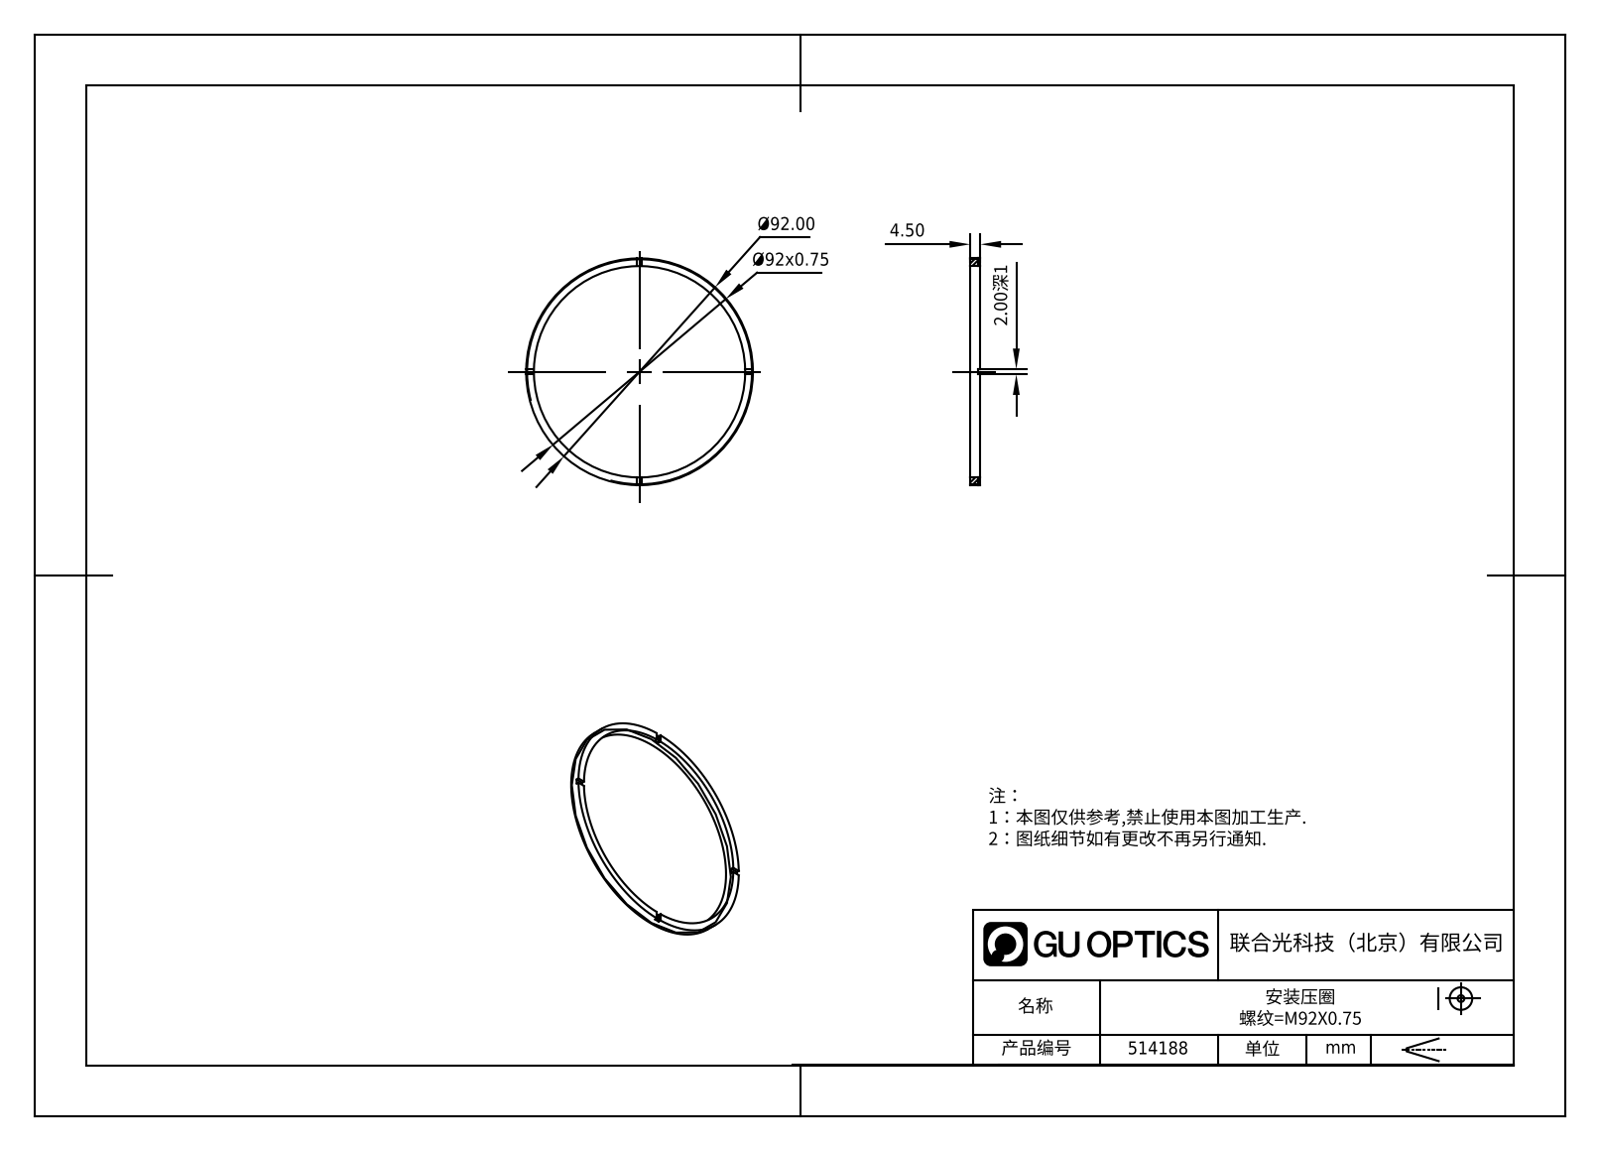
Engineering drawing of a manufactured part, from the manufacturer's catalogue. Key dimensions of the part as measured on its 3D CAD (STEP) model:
Part name (STEP PRODUCT): 514188
STEP written by: SolidWorks 2020 (CONFIG_CONTROL_DESIGN)
Units: millimetres
Bodies: 1 solid, 21 faces (17 planar, 4 cylindrical, 0 other)
Overall size (bounding box): 92 × 92 × 4.5
Volume: 4 351 mm³ · Surface area: 4 460 mm²
Round holes (diameter × count): ⌀85 ×1
Round bosses / shafts (diameter × count): ⌀92 ×1
Main face-to-face distances: 4.5, 3.5, 1, 2
